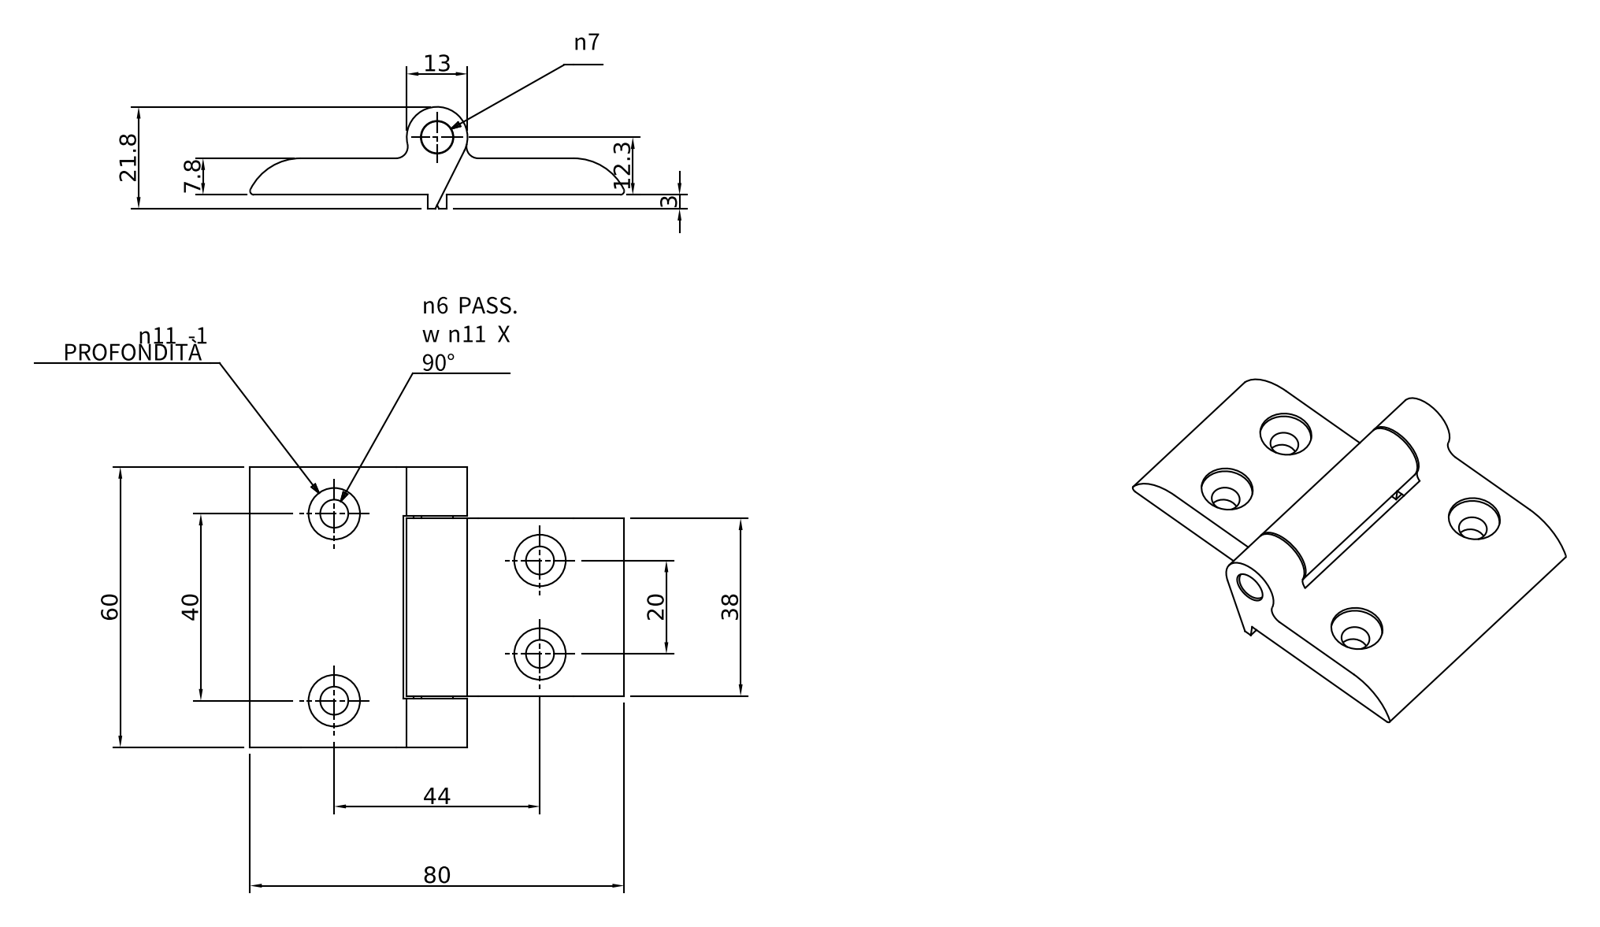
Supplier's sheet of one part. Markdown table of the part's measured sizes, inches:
| quantity | value |
| --- | --- |
| part name | CCRYY0000017; 440000016423; 440000016424; 958510007799 |
| STEP written by | Autodesk Inventor 2019 (AUTOMOTIVE_DESIGN) |
| units | inches |
| bodies | 3 solids, 49 faces (22 planar, 19 cylindrical, 8 other) |
| overall size | 3.15 × 2.362 × 0.858 |
| volume | 2.089 in³ |
| surface area | 23.47 in² |
| round holes (diameter × count) | 0.236 × 4, 0.433 × 4, 0.276 × 1 |
| round bosses / shafts (diameter × count) | 0.268 × 1 |
| partial cylindrical surfaces (radius × count) | 0.098 × 2, 0.472 × 2, 0.256 × 1 |
| main face-to-face distances | 0.307, 0.433, 1.929, 2.362, 1.496, 0.413, 1.949, 0.02, 1.516, 1.535 |
| hole center spacings | 1.776, 2.096, 0.787, 1.575 |
